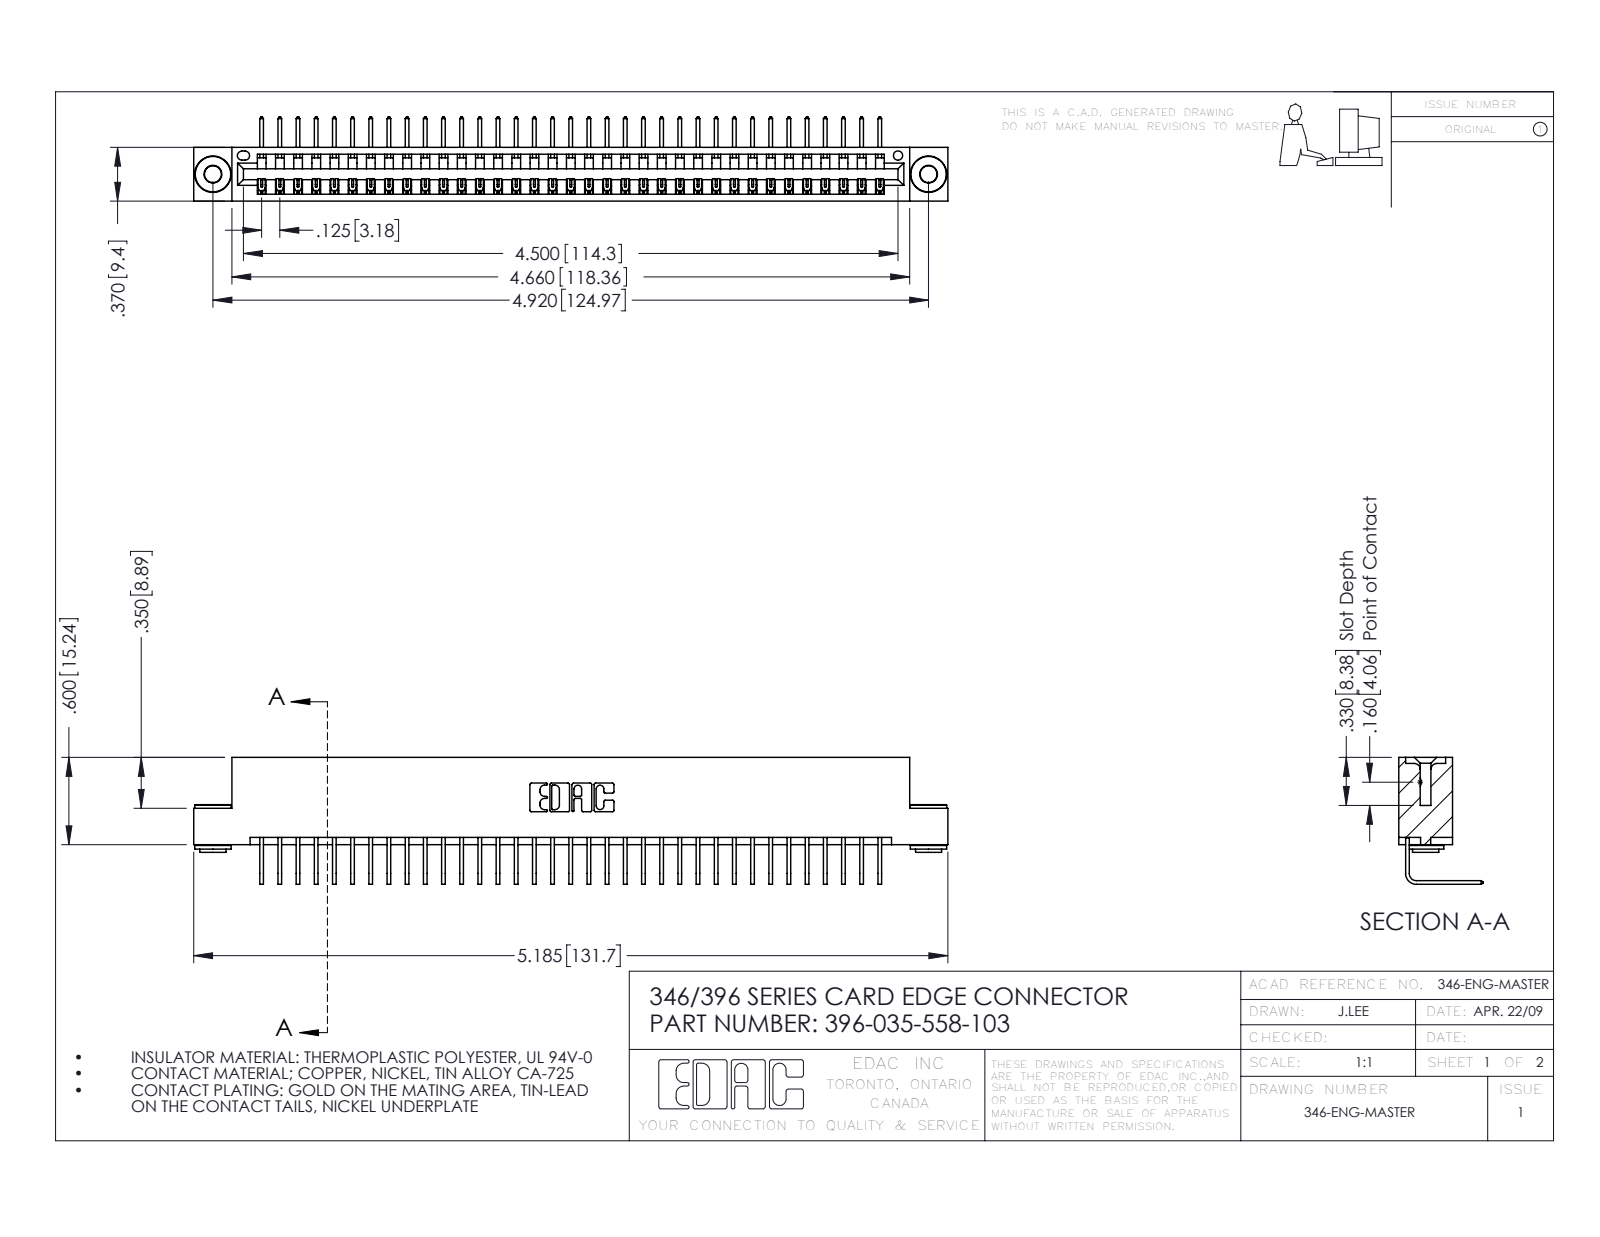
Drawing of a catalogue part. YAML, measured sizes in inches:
part_name: "396-035-558-103; 345-250-002_345-250-002-102; 345-292-001_558 Tail - 2; 346 Part_Flush Mounting Lugs - 0.156 Dia-TH"
step_written_by: "SolidWorks 2016 (CONFIG_CONTROL_DESIGN)"
units: inches
bodies: {solids: 38, faces: 2260, planar: 1556, cylindrical: 696, other: 8}
overall_size: [5.185, 0.873, 0.58]
volume: 0.775
surface_area: 25.89
round_holes:
  - {diameter: 0.116, count: 2}
  - {diameter: 0.156, count: 2}
  - {diameter: 0.064, count: 1}
round_bosses_or_shafts:
  - {diameter: 0.25, count: 2}
  - {diameter: 0.18, count: 2}
  - {diameter: 0.136, count: 2}
partial_cylinders:
  - {radius: 0.006, count: 70}
  - {radius: 0.01, count: 22}
  - {radius: 0.007, count: 6}
  - {radius: 0.031, count: 6}
  - {radius: 0.026, count: 3}
  - {radius: 0.031, count: 2}
  - {radius: 0.04, count: 2}
  - {radius: 0.014, count: 1}
face_to_face_distances: [0.322, 0.048, 0.37, 0.25, 0.025, 0.298, 0.072, 0.148, 0.222, 0.1]
hole_center_spacings: [0.246, 4.711, 4.92]
